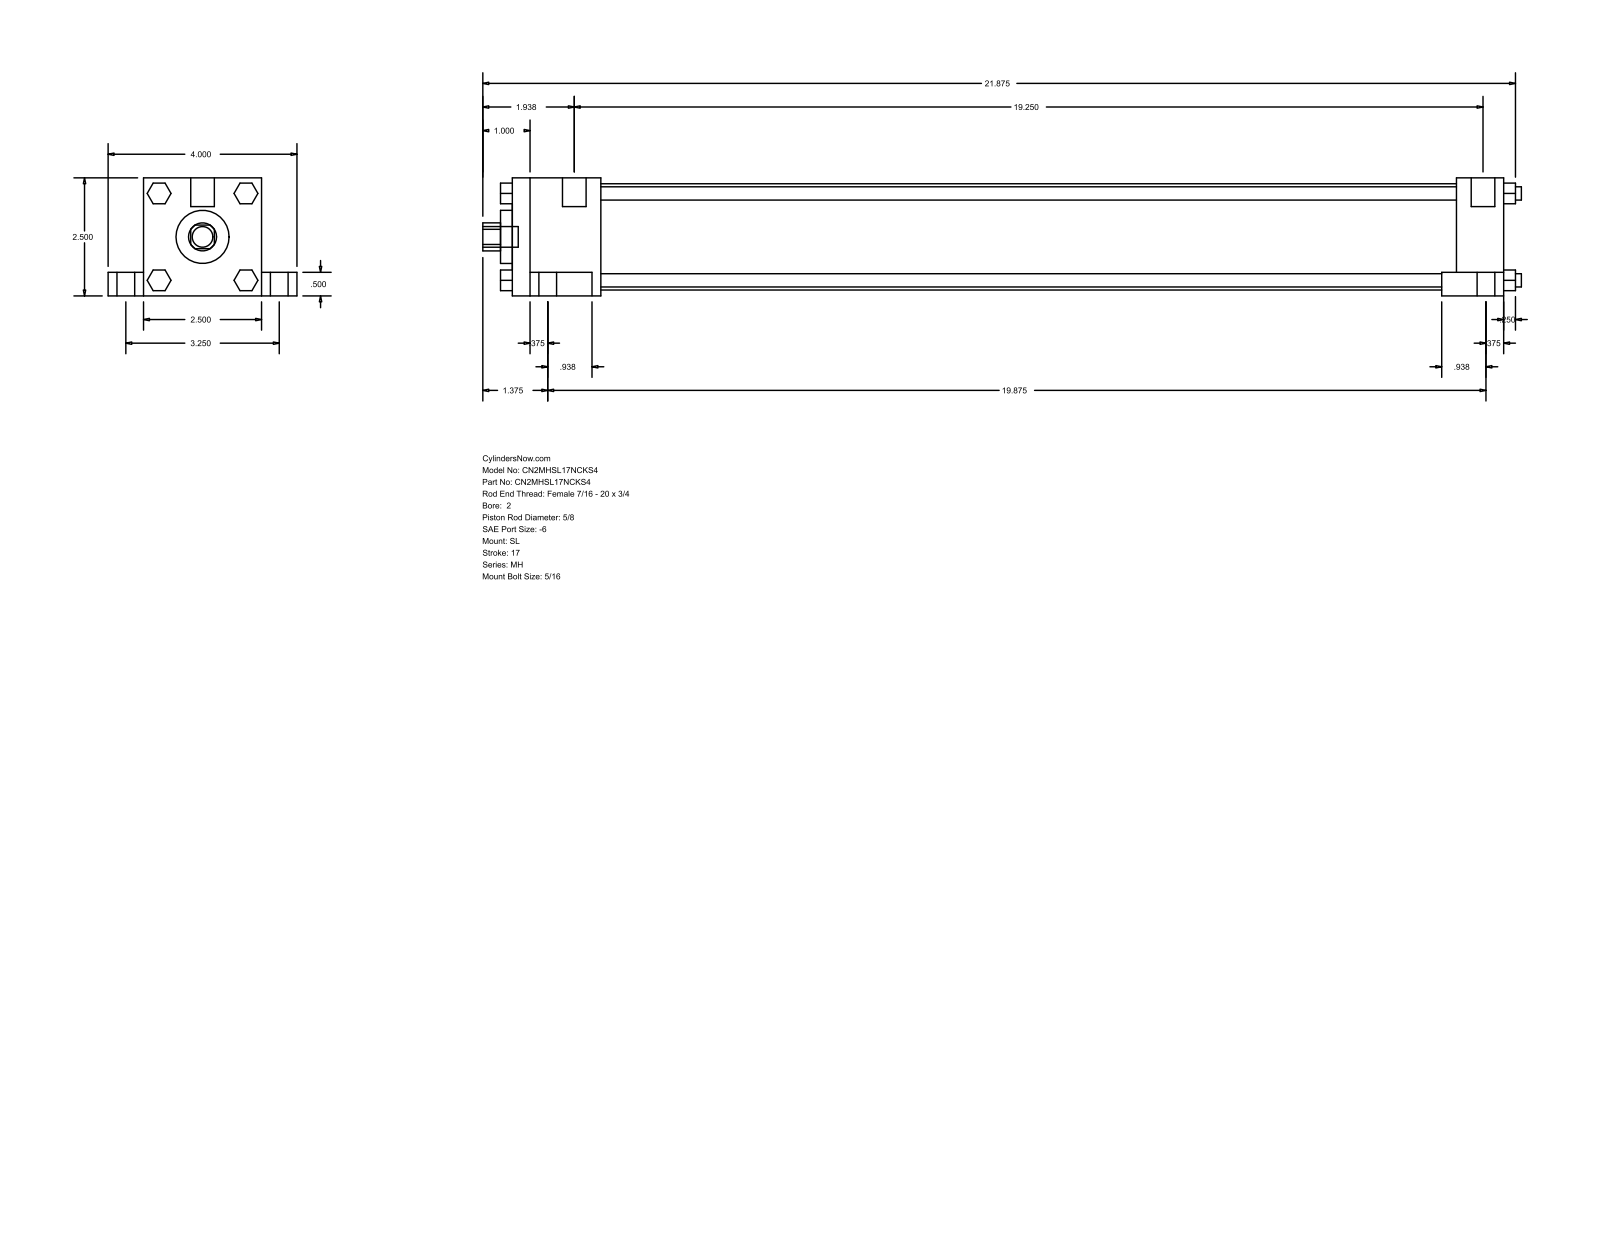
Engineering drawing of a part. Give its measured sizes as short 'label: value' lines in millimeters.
name: MH_SL__0200_0.625
written by: GSSL Pune (CONFIG_CONTROL_DESIGN)
unit: mm
bodies: 0 solids, 148 faces (112 planar, 36 cylindrical, 0 other)
size: 558.8 × 101.6 × 63.5
holes: 1× ⌀15.88, 1× ⌀28.57, 1× ⌀57.15
bosses: 4× ⌀15.88, 4× ⌀9.53, 4× ⌀7.14, 4× ⌀5.56, 2× ⌀12.7, 1× ⌀11.11
rounds: 1× R7.54
face distances: 63.5, 533.39, 12.7, 19.05, 50.8, 82.55, 508, 25.39, 47.62, 460.38
